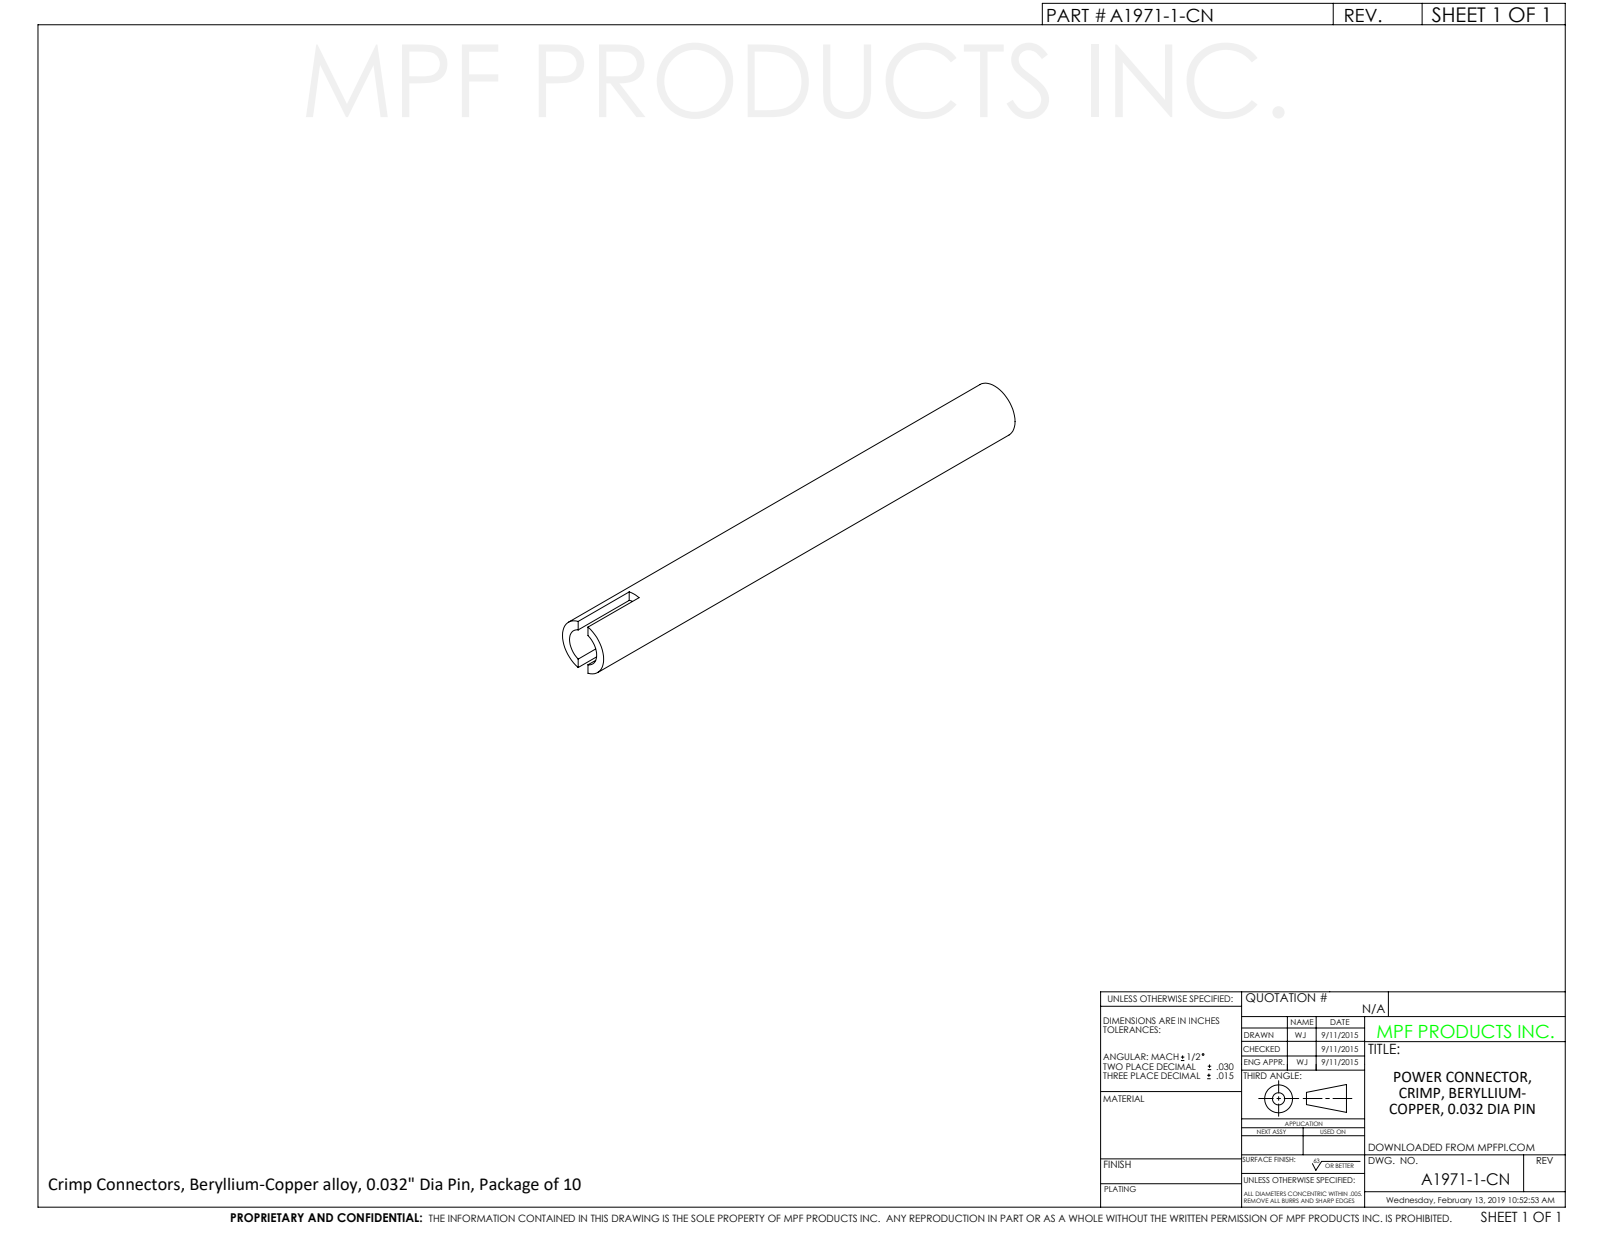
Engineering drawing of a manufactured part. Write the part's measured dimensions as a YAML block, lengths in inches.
part_name: "A1971-1-CN"
step_written_by: "SolidWorks 2012 (CONFIG_CONTROL_DESIGN)"
units: inches
bodies: {solids: 1, faces: 13, planar: 9, cylindrical: 4, other: 0}
overall_size: [0.5, 0.05, 0.05]
volume: 0.001
surface_area: 0.132
round_holes:
  - {diameter: 0.033, count: 1}
round_bosses_or_shafts:
  - {diameter: 0.05, count: 1}
face_to_face_distances: [0.5, 0.438, 0.062]
